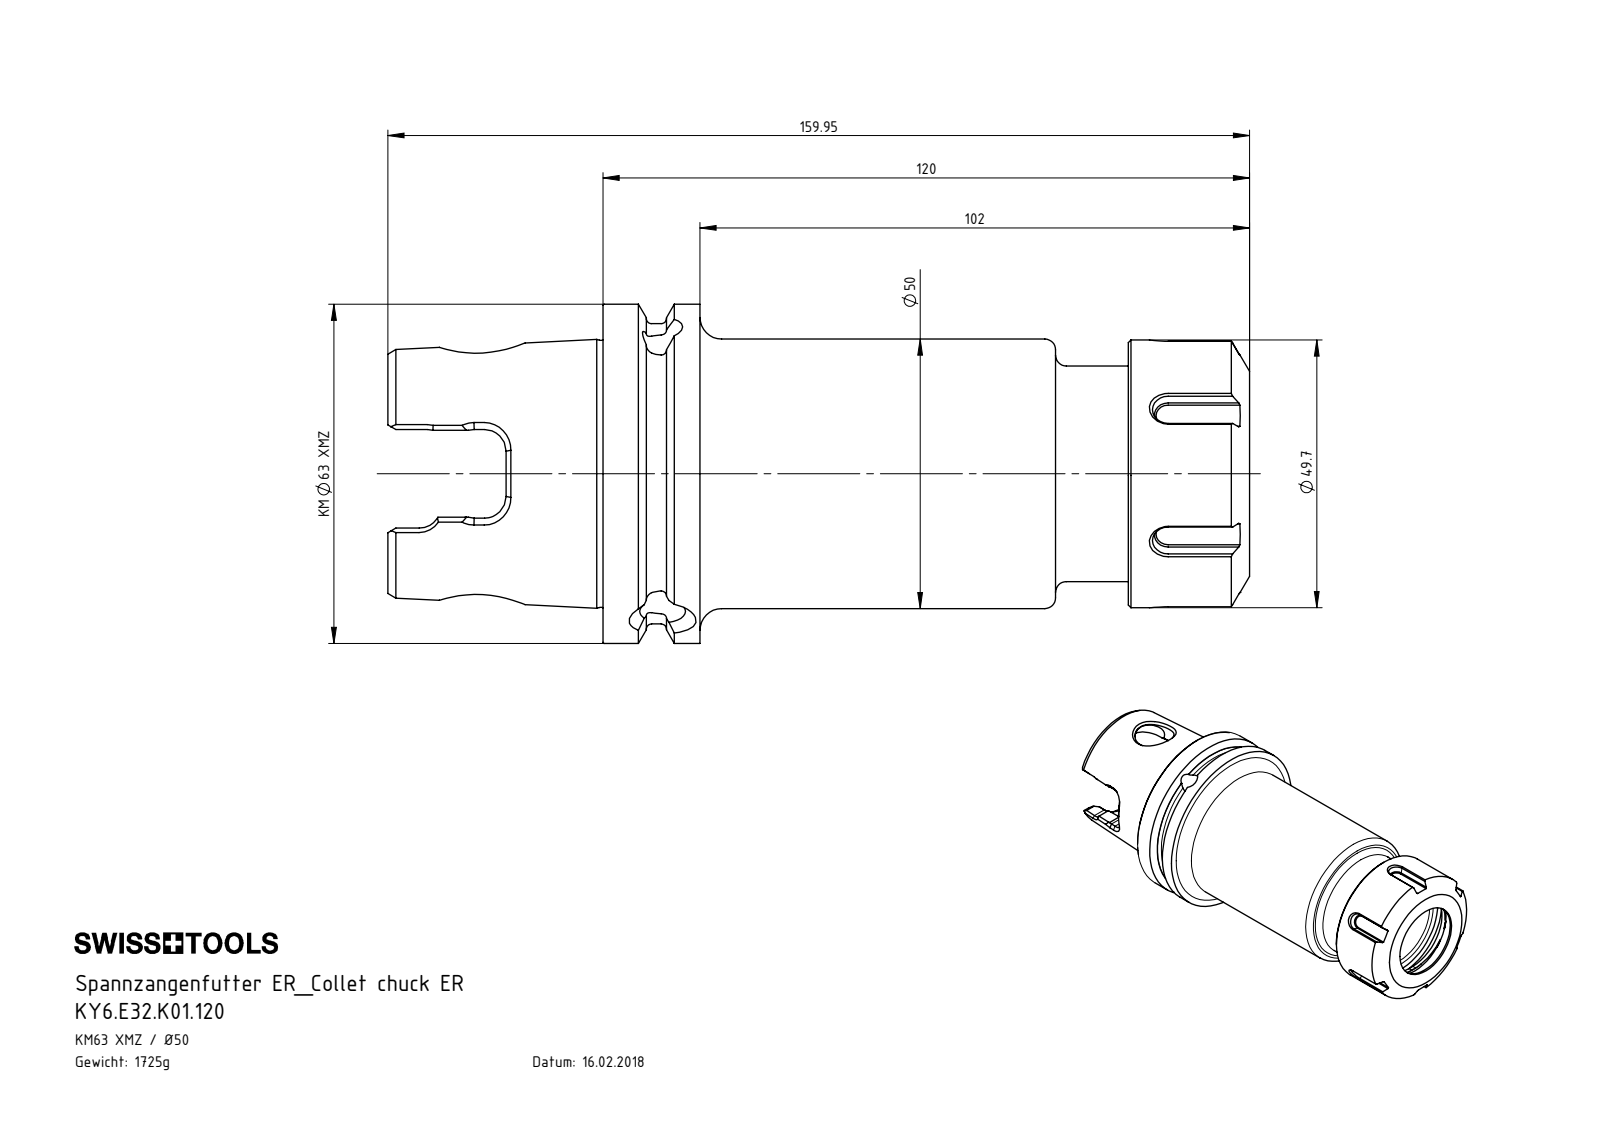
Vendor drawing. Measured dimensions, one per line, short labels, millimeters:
name: KY6-E32.K01.120_B; KY6.E32.K01.120; E32-ER1.001.022
written by: SolidWorks 2017 (CONFIG_CONTROL_DESIGN)
unit: mm
bodies: 2 solids, 324 faces (100 planar, 68 cylindrical, 156 other)
size: 159.95 × 62.95 × 62.95
volume: 219 775 mm³; area: 46 983 mm²
holes: 2× ⌀7.47, 1× ⌀8, 1× ⌀8.48, 1× ⌀10, 1× ⌀11.5, 1× ⌀14.5, 1× ⌀20.5, 1× ⌀24, 1× ⌀27.1, 1× ⌀31.1, 1× ⌀35.27, 1× ⌀36.5
bosses: 1× ⌀62.95, 1× ⌀55.7, 1× ⌀50, 1× ⌀49.7, 1× ⌀40
rounds: 6× R4, 2× R7.04, 2× R15.5
face distances: 97.5, 1.1, 98.6, 121.1, 120, 22.5, 18, 102, 19.1, 79.5
